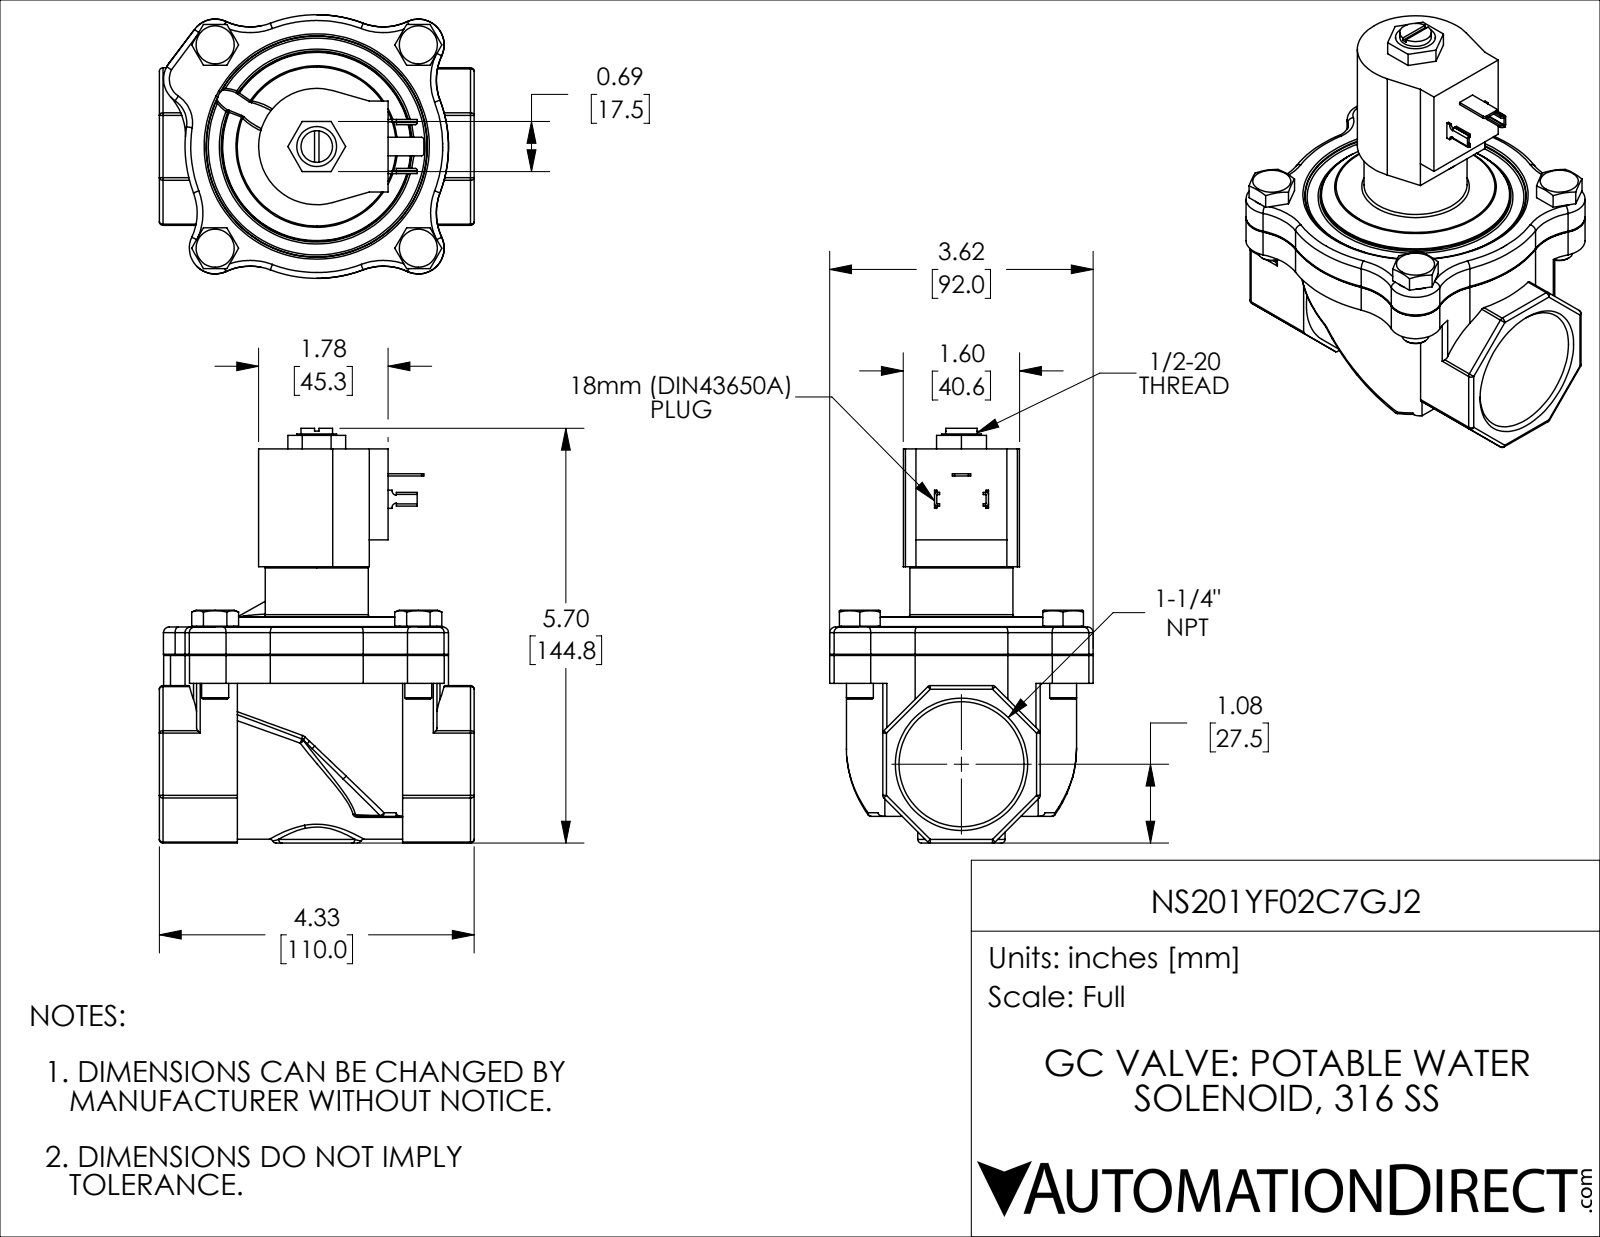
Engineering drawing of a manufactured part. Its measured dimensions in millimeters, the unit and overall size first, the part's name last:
Units: millimetres
Overall size (bounding box): 144.8 × 110 × 92
Round holes (diameter × count): ⌀9.5 ×4, ⌀11 ×4, ⌀3.2 ×1, ⌀12.4 ×1, ⌀21.5 ×1, ⌀24.1 ×1, ⌀43.6 ×1
Round bosses / shafts (diameter × count): ⌀12.8 ×4, ⌀9.4 ×4, ⌀36 ×1, ⌀13.9 ×1, ⌀11 ×1
Partial cylindrical surfaces — rounded edges, fillets, slot ends (radius × count): R1.3 ×30, R20 ×15, R0.8 ×8, R9 ×8, R9.2 ×2, R46 ×2, R0.8 ×1, R2 ×1
Main face-to-face distances: 10, 72.1, 62.2, 31, 21, 41.1, 65.5, 75.4, 96.5, 137.6
Hole centre spacings: 71, 50.2, 50.2, 71, 71, 100.4, 100.4
Volume: 443 400 mm³ · Surface area: 88 710 mm²
Bodies: 12 solids, 524 faces (166 planar, 159 cylindrical, 199 other)
Part name (STEP PRODUCT): NS201YF02C7GJ2
STEP written by: SolidWorks 2018 (AUTOMOTIVE_DESIGN)
